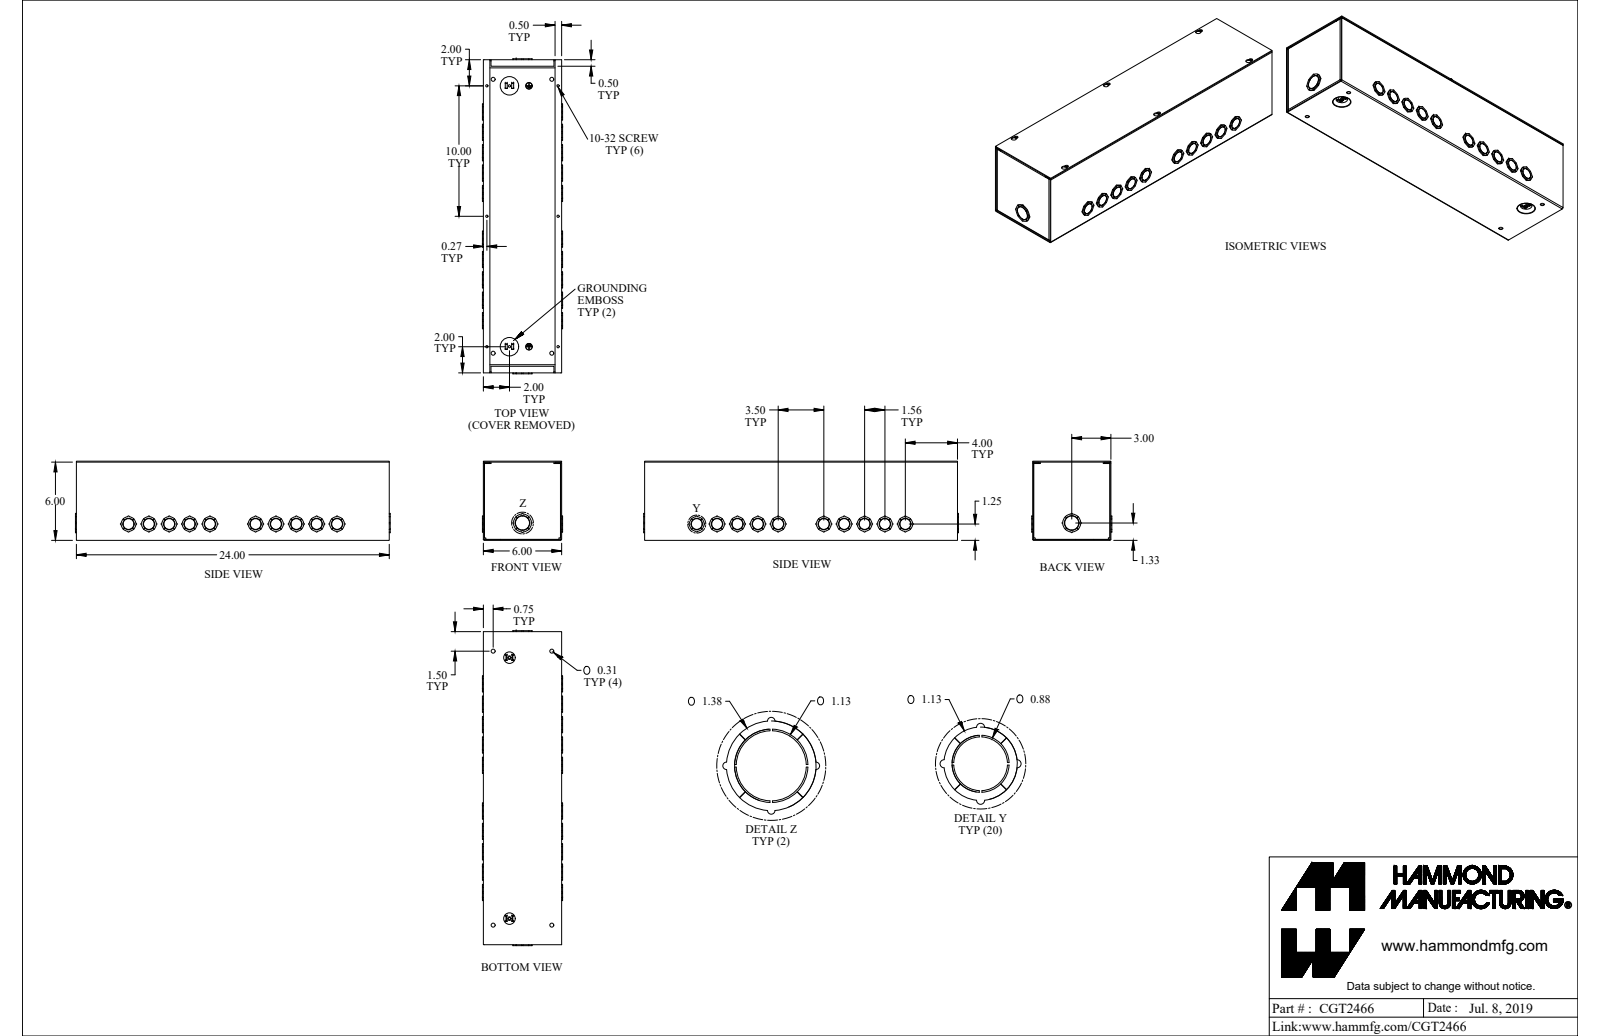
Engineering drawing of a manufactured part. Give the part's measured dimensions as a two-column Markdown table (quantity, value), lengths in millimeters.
| quantity | value |
| --- | --- |
| part name | CGT2466 |
| STEP written by | SolidWorks 2021 (AUTOMOTIVE_DESIGN) |
| units | millimeters |
| bodies | 6 solids, 1198 faces (582 planar, 602 cylindrical, 14 other) |
| overall size | 613.3 × 158.7 × 156.1 |
| volume | 721 000 mm³ |
| surface area | 900 600 mm² |
| round holes (diameter × count) | 22.2 × 10, 4.3 × 8, 7.9 × 4, 12.7 × 2, 28.6 × 1 |
| round bosses / shafts (diameter × count) | 28.6 × 10, 21 × 10, 12.5 × 2, 7.2 × 2, 4.8 × 2, 34.9 × 1, 27.3 × 1, 9.5 × 1 |
| partial cylindrical surfaces (radius × count) | 1.6 × 40, 0.9 × 8, 1.4 × 8, 2.7 × 8, 3.2 × 6, 5.2 × 6, 0.7 × 4, 1.4 × 4 |
| main face-to-face distances | 1.4, 151, 152.4, 1.8, 149.5, 154.2, 152.8, 607.8, 3.3, 609.6 |
| hole center spacings | 79.3, 17.6, 39.7, 39.7, 127.1, 207.9, 254, 267 |
